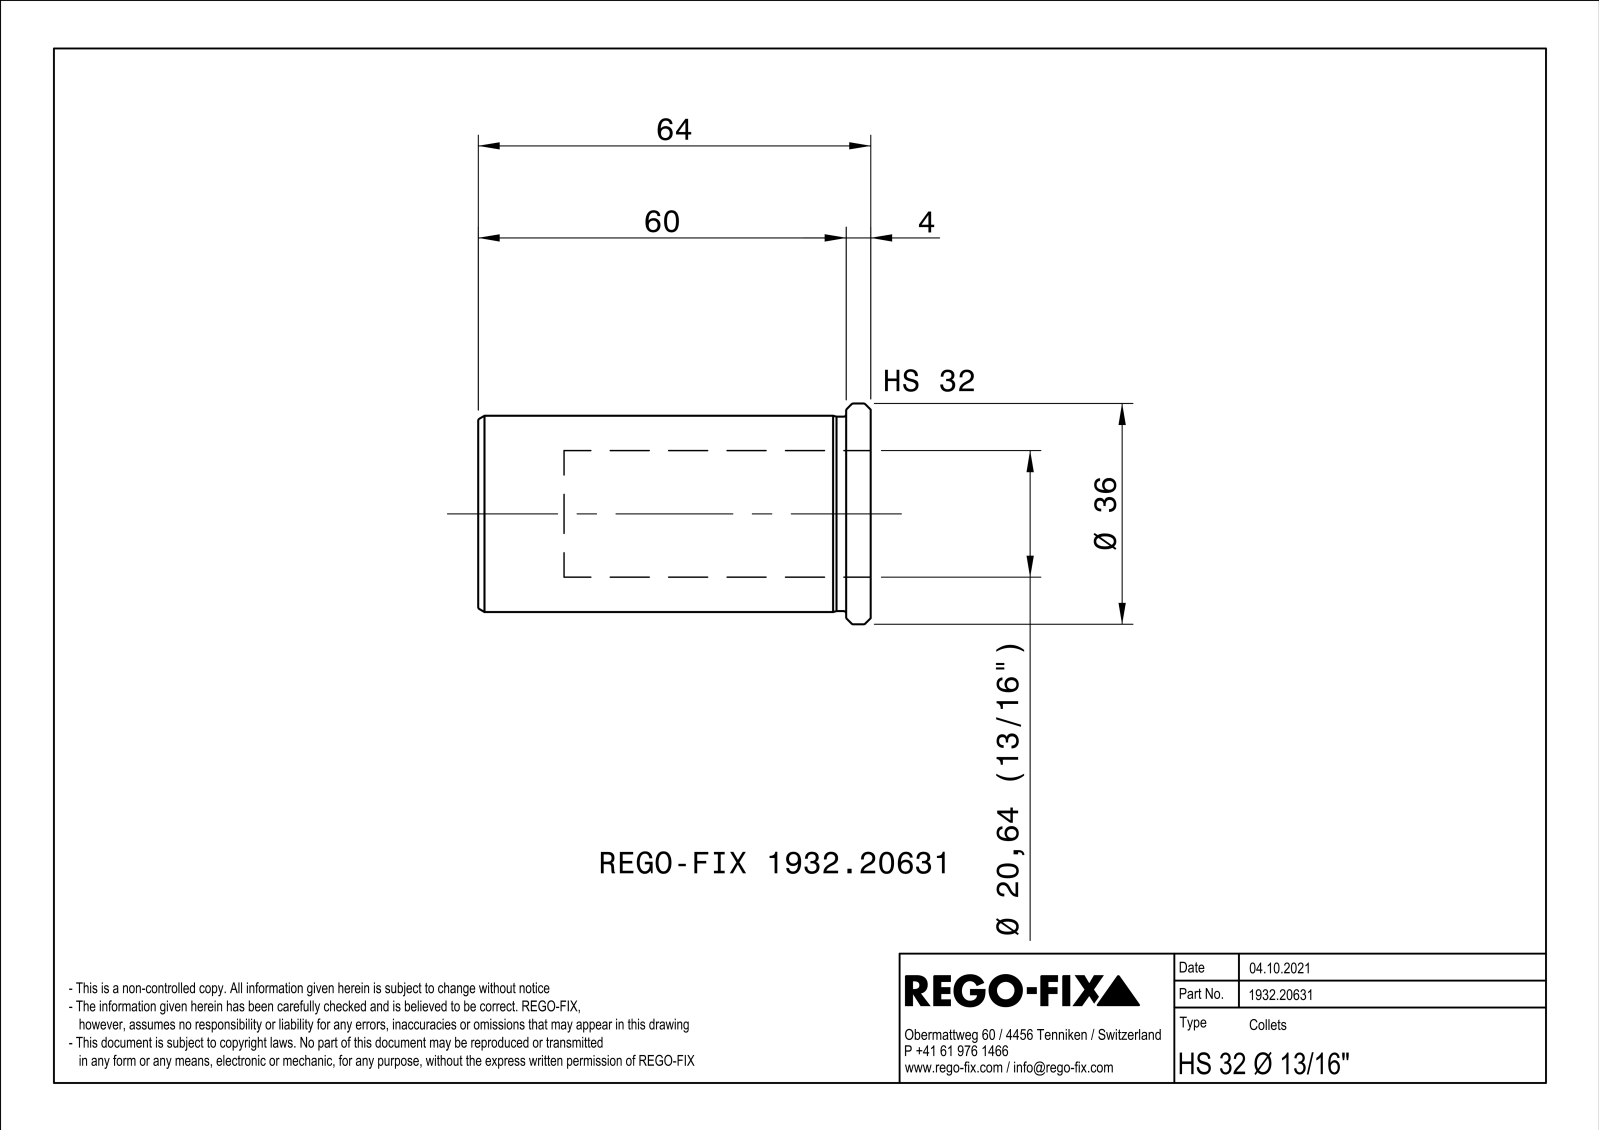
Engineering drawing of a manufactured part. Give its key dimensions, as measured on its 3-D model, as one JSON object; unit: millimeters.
{"part_name": "NOCUT", "step_written_by": "SIEMENS PLM Software Solid Edge ST10 (AUTOMOTIVE_DESIGN)", "units": "millimeters", "bodies": {"solids": 1, "faces": 70, "planar": 22, "cylindrical": 11, "other": 37}, "overall_size": [64, 35.99, 35.99], "volume_mm3": 27009, "surface_area_mm2": 13634, "round_holes": [[20.64, 1], [26.5, 1]], "round_bosses_or_shafts": [[36, 1], [32, 1], [31.7, 1]], "face_to_face_distances": [1, 64, 4, 60]}
